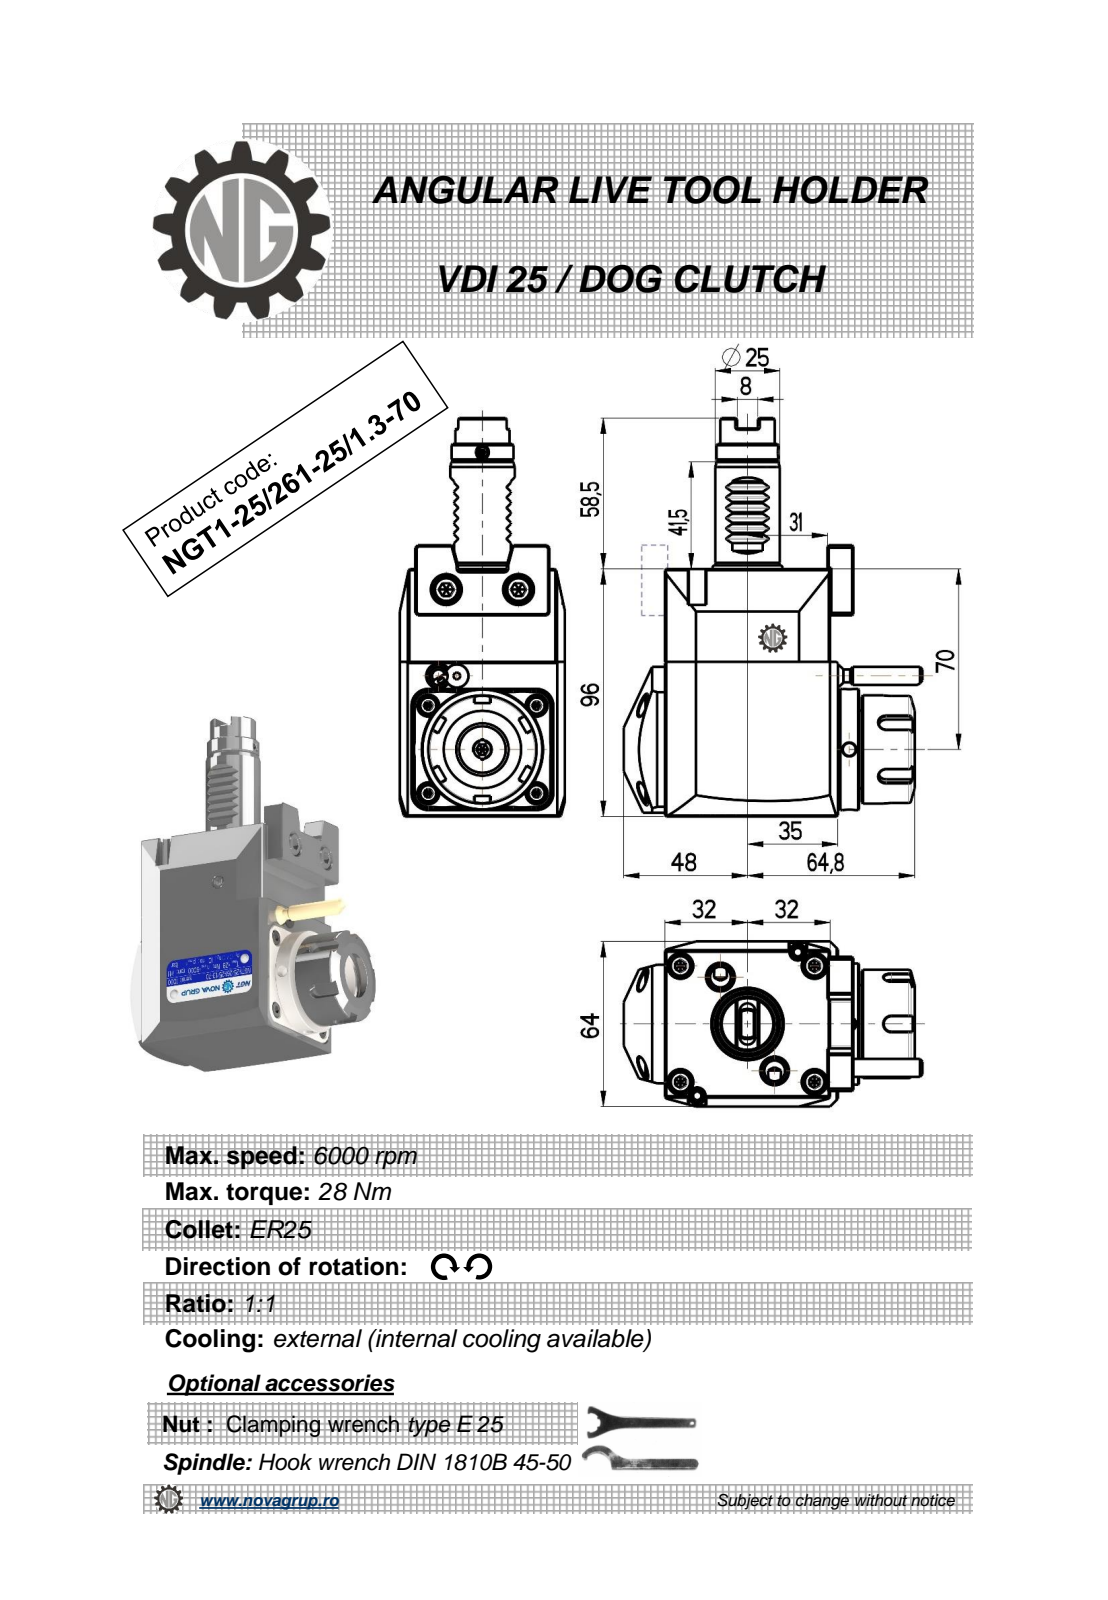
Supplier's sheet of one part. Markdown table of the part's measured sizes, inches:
| quantity | value |
| --- | --- |
| part name | NGT1_25_261_25_1_3_70 |
| STEP written by | PRO/ENGINEER BY PARAMETRIC TECHNOLOGY CORPORATION, 2010280 (CONFIG_CONTROL_DESIGN) |
| units | inches |
| bodies | 1 solid, 430 faces (218 planar, 70 cylindrical, 142 other) |
| overall size | 6.083 × 4.56 × 2.52 |
| volume | 30.4 in³ |
| surface area | 76.26 in² |
| round holes (diameter × count) | 0.197 × 2, 0.098 × 1, 0.118 × 1, 0.799 × 1 |
| round bosses / shafts (diameter × count) | 1.85 × 1, 1.654 × 1, 1.378 × 1, 1.299 × 1, 0.984 × 1, 0.945 × 1, 0.827 × 1, 0.742 × 1 |
| partial cylindrical surfaces (radius × count) | 0.012 × 12, 0.01 × 6, 0.118 × 5, 0.138 × 4, 0.02 × 2, 0.039 × 2, 1.26 × 1 |
| main face-to-face distances | 2.52, 3.78, 0.236, 0.354, 2.646, 0.118, 0.126, 2.874, 0.228, 0.315 |
| hole center spacings | 1.307 |
